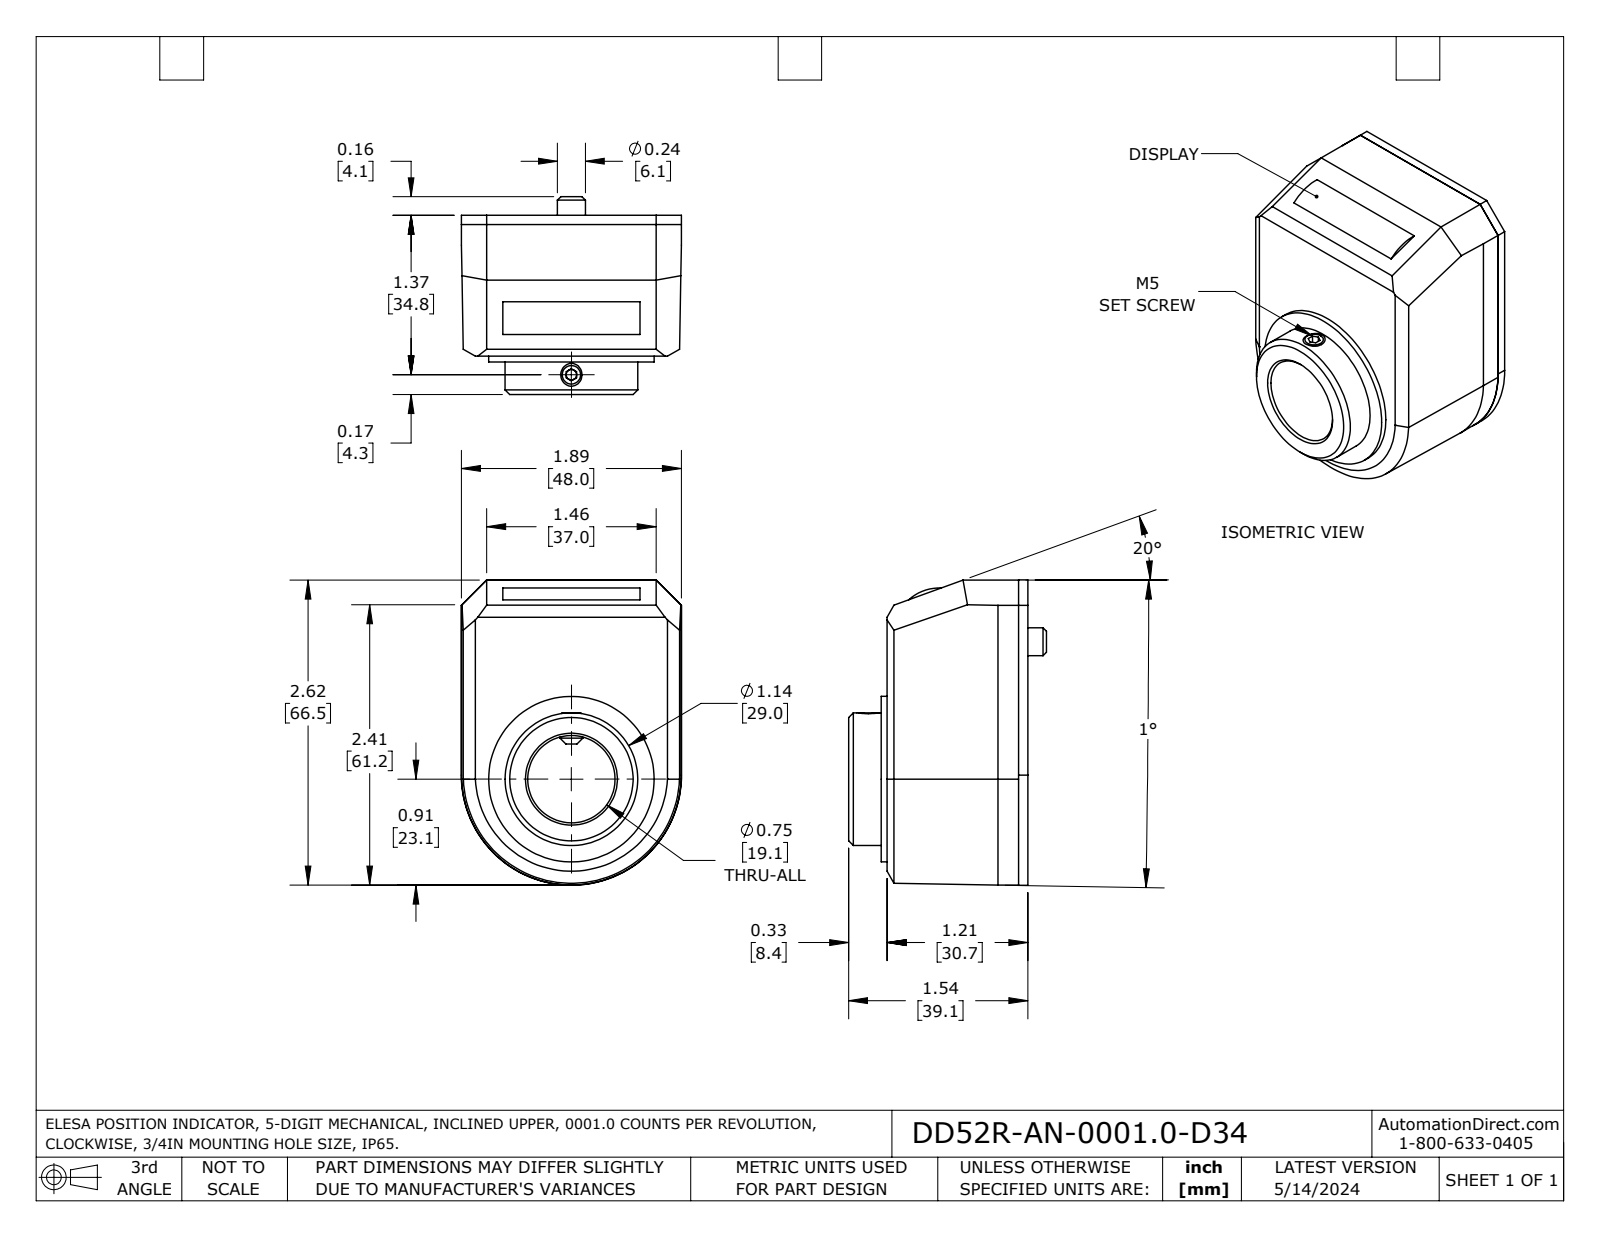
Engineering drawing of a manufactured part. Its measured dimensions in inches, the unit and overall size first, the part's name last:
Units: inches
Overall size (bounding box): 2.622 × 1.892 × 1.7
Round holes (diameter × count): ⌀0.163 ×1, ⌀0.75 ×1, ⌀0.945 ×1, ⌀1.57 ×1, ⌀1.58 ×1
Round bosses / shafts (diameter × count): ⌀1.422 ×1, ⌀1.14 ×1, ⌀0.24 ×1, ⌀0.197 ×1
Partial cylindrical surfaces — rounded edges, fillets, slot ends (radius × count): R0.39 ×1, R0.945 ×1, R0.946 ×1
Main face-to-face distances: 1.21, 1.051, 0.159, 0.05, 1.101, 1.26, 0.28, 0.33, 1.381, 1.54
Volume: 4.683 in³ · Surface area: 28.91 in²
Bodies: 3 solids, 68 faces (46 planar, 13 cylindrical, 9 other)
Part name (STEP PRODUCT): DD52R-AN-INCH
STEP written by: SolidWorks 2023 (AUTOMOTIVE_DESIGN)
